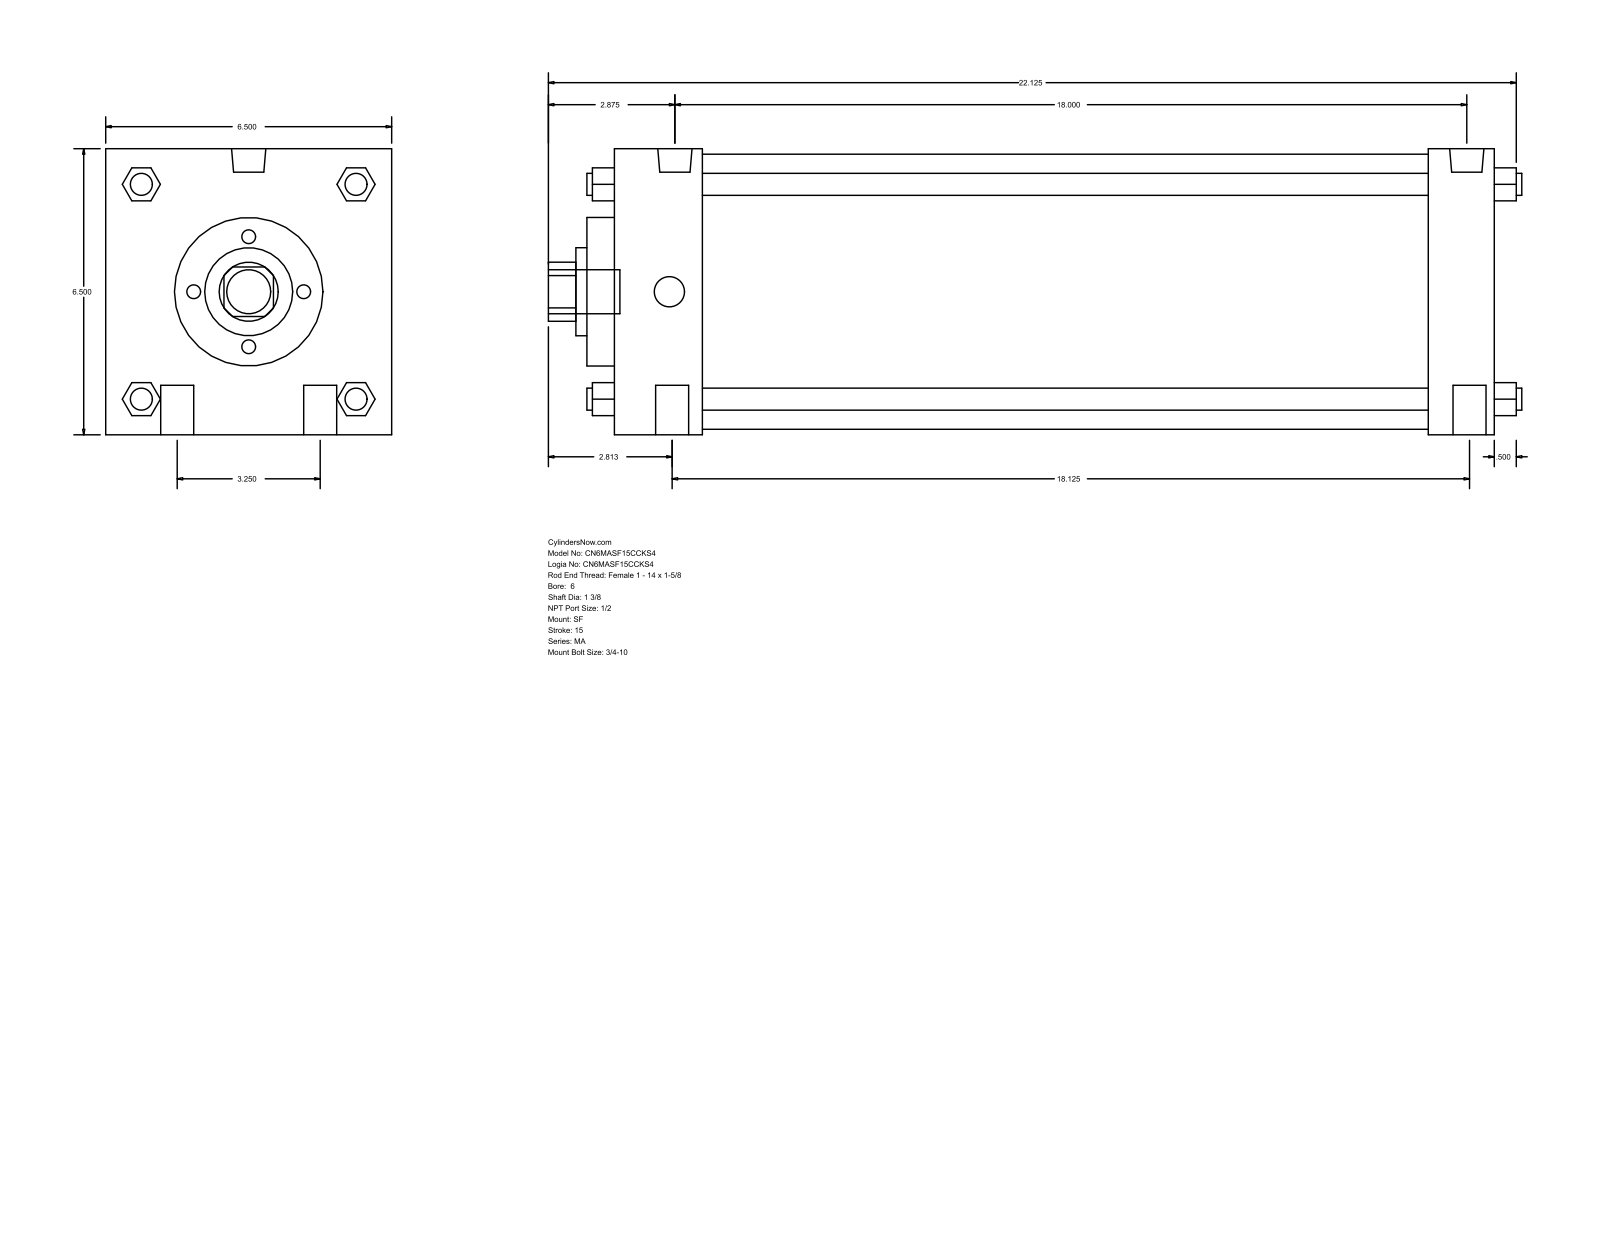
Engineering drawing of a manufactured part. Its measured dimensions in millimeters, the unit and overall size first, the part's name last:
Units: millimetres
Overall size (bounding box): 561.98 × 165.1 × 165.1
Round holes (diameter × count): ⌀34.92 ×1, ⌀50.8 ×1, ⌀85.72 ×1, ⌀158.75 ×1
Round bosses / shafts (diameter × count): ⌀19.05 ×4, ⌀12.7 ×4, ⌀19.77 ×2, ⌀17.46 ×2, ⌀25.4 ×1
Partial cylindrical surfaces — rounded edges, fillets, slot ends (radius × count): R17.06 ×1
Main face-to-face distances: 165.1, 508, 469.9, 50.8, 38.1, 419.1, 457.2, 15.87, 66.67, 485.77
Bodies: 0 solids, 126 faces (95 planar, 31 cylindrical, 0 other)
Part name (STEP PRODUCT): MA_SF__0600_1.375
STEP written by: GSSL Pune (CONFIG_CONTROL_DESIGN)
